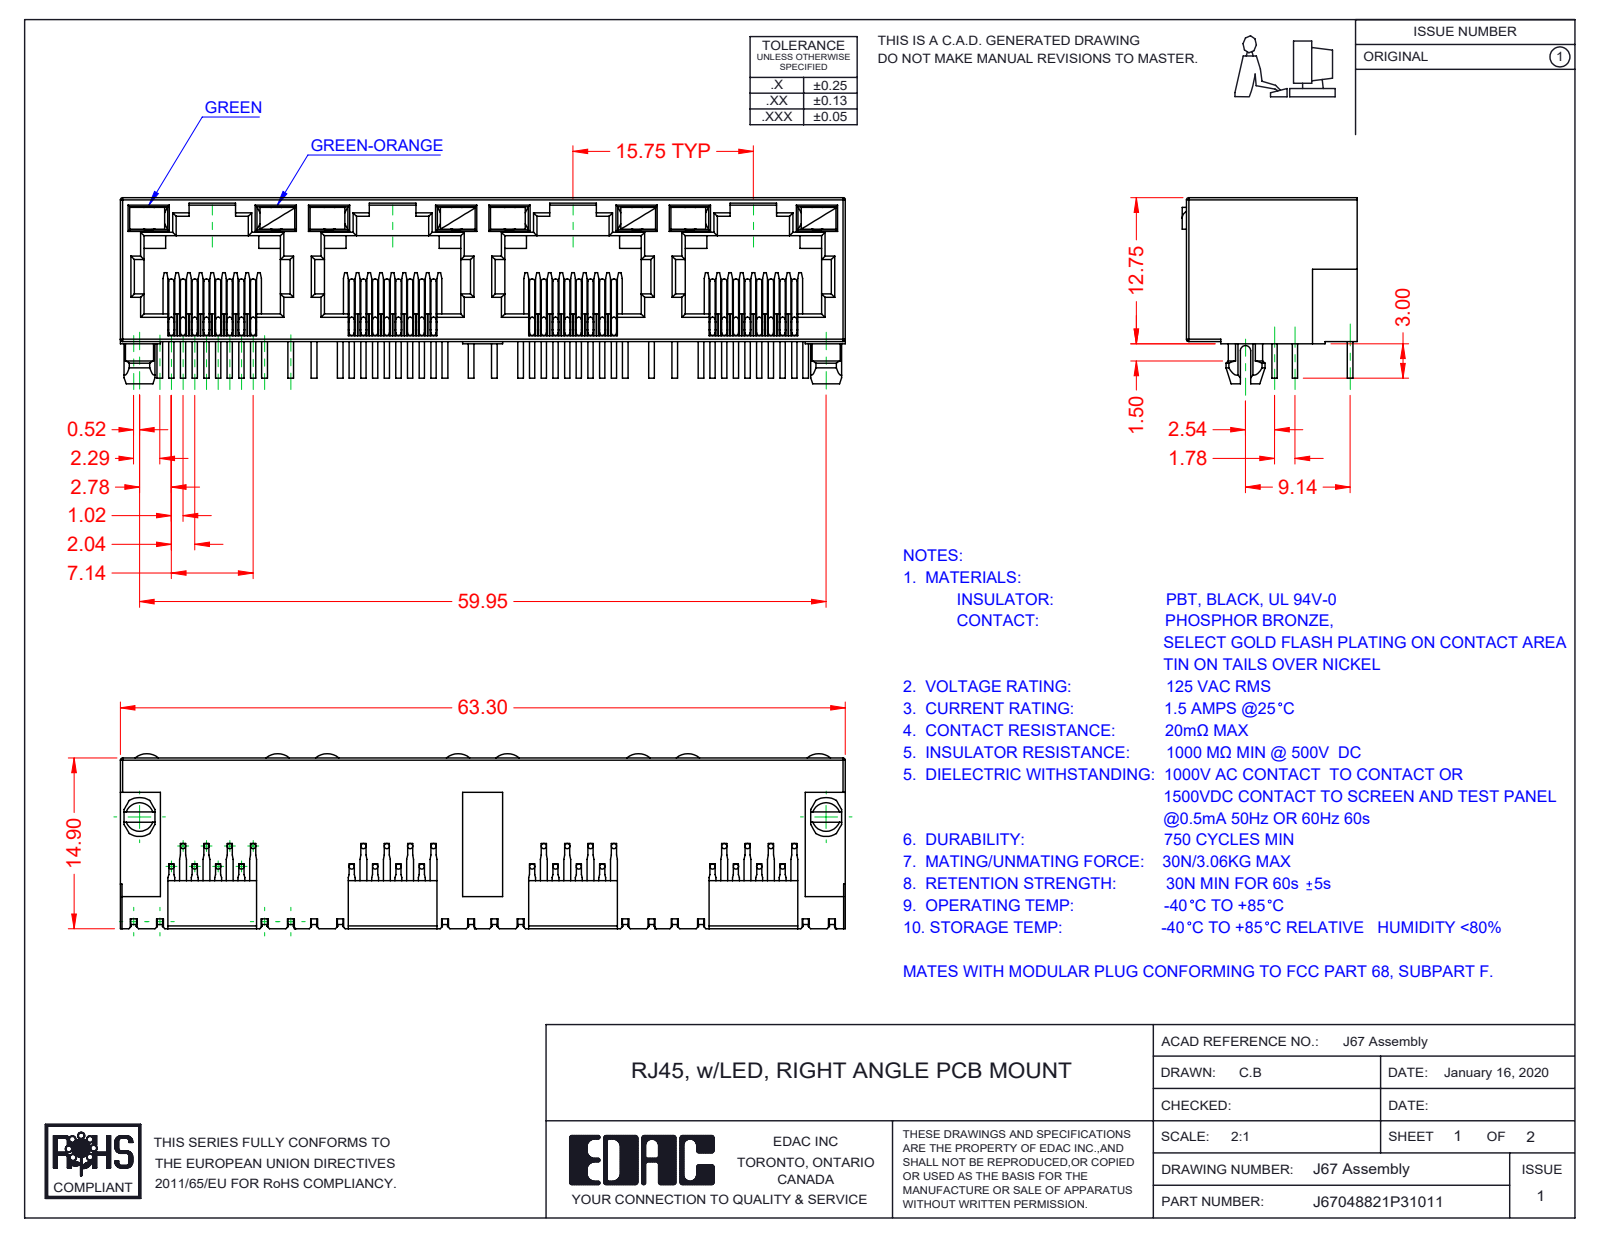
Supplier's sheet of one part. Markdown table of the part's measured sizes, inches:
| quantity | value |
| --- | --- |
| part name | 67 LED RH_7-Green-Orange; 67 LED LH_3-Green; 67 Contacts; 67 Insulator (+1 more) |
| STEP written by | SolidWorks 2016 (CONFIG_CONTROL_DESIGN) |
| units | inches |
| bodies | 41 solids, 2473 faces (1781 planar, 484 cylindrical, 208 other) |
| overall size | 2.492 × 0.64 × 0.602 |
| volume | 0.315 in³ |
| surface area | 17.94 in² |
| round bosses / shafts (diameter × count) | 0.018 × 96 |
| partial cylindrical surfaces (radius × count) | 0.008 × 66, 0.012 × 29, 0.018 × 9, 0.061 × 8, 0.059 × 2, 0.067 × 2, 0.014 × 1, 0.039 × 1 |
| main face-to-face distances | 0.02, 0.494, 0.074, 0.035, 0.394, 0.62, 0.039, 0.055, 0.433, 0.468 |
